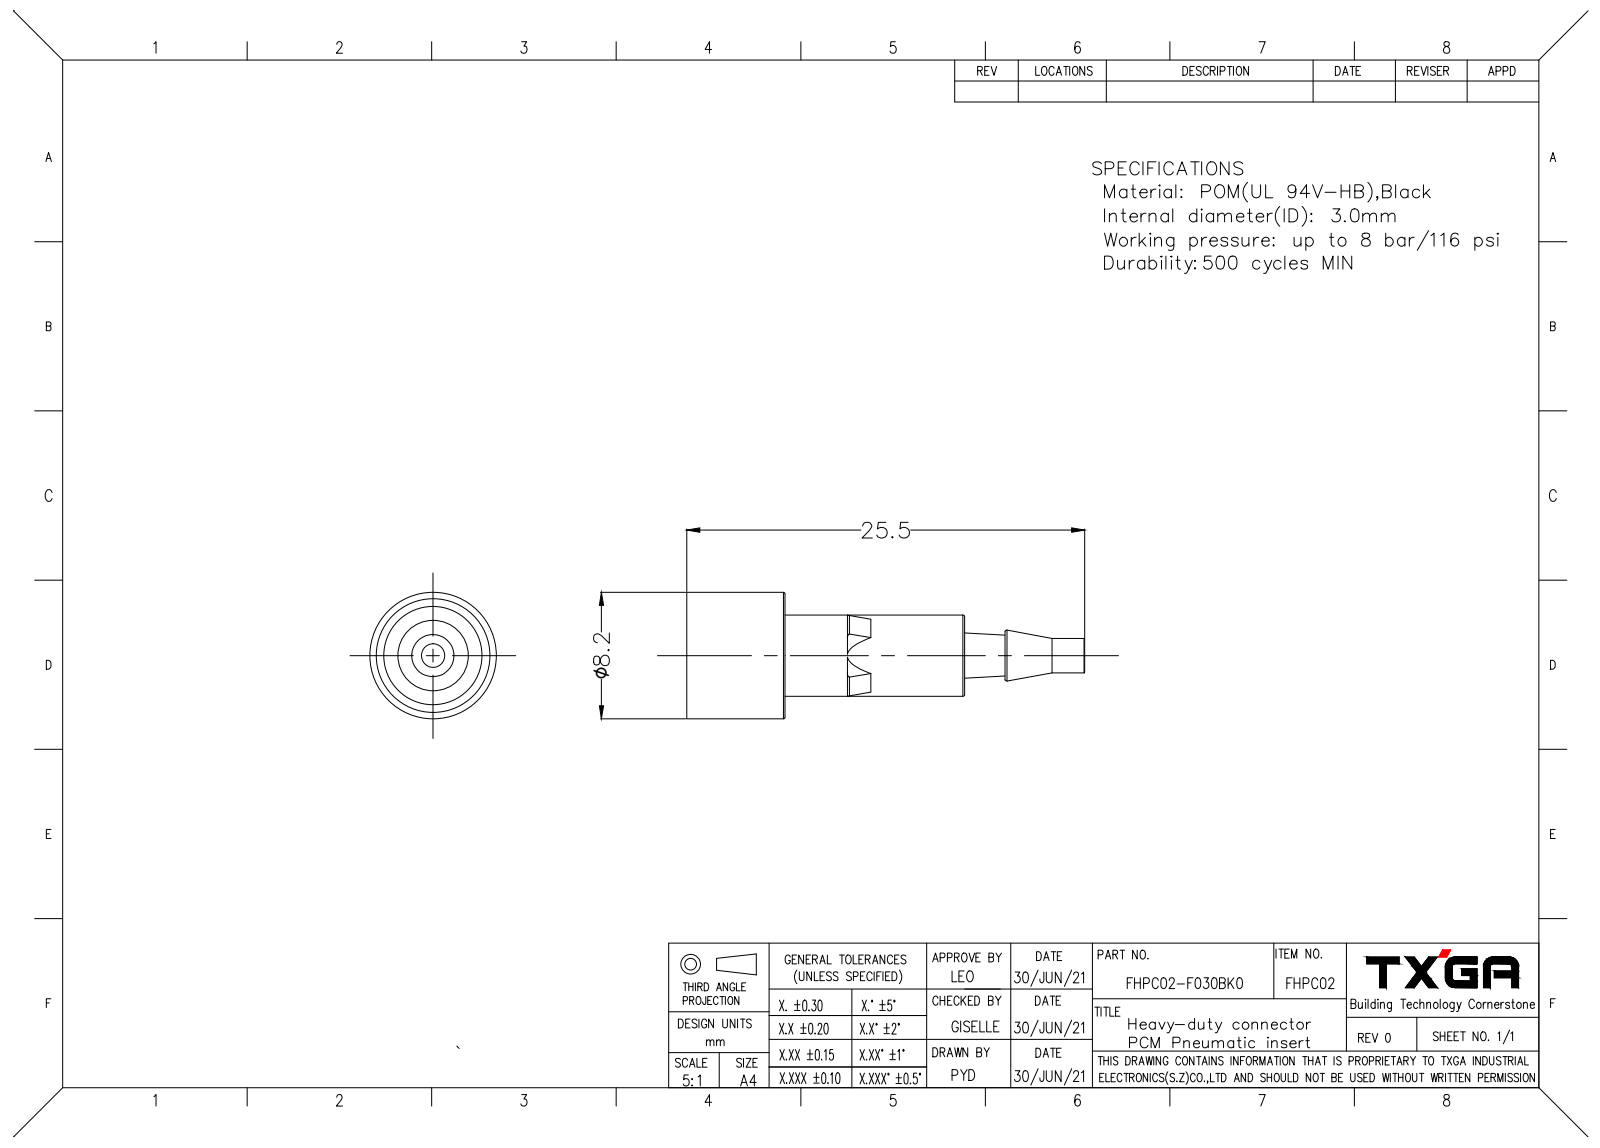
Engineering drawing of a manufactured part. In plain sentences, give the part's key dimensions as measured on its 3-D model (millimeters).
The part is named "Admi16F8F3C4yurm". Its 3-D file was written by "SIEMENS PLM Software NX 10.0 (AUTOMOTIVE_DESIGN)". It is 1 solid with 95 faces: 49 planar, 22 cylindrical and 24 other. Overall it measures 25.4 by 8.2 by 8.2 millimeters. Its volume is 372 cubic millimeters and its surface area 871 square millimeters. Round holes: 1 of diameter 1.5, 1 of diameter 2.6, 1 of diameter 6.35. Round bosses or shafts: 1 of diameter 8.2, 1 of diameter 5.3, 1 of diameter 4.4, 1 of diameter 2.78, 1 of diameter 1.69. The main face-to-face distances are 1.1, 0.6, 5.2, 6.3, 17.9, 12.7, 11.6, 0.69, 6.5, 1.3.
